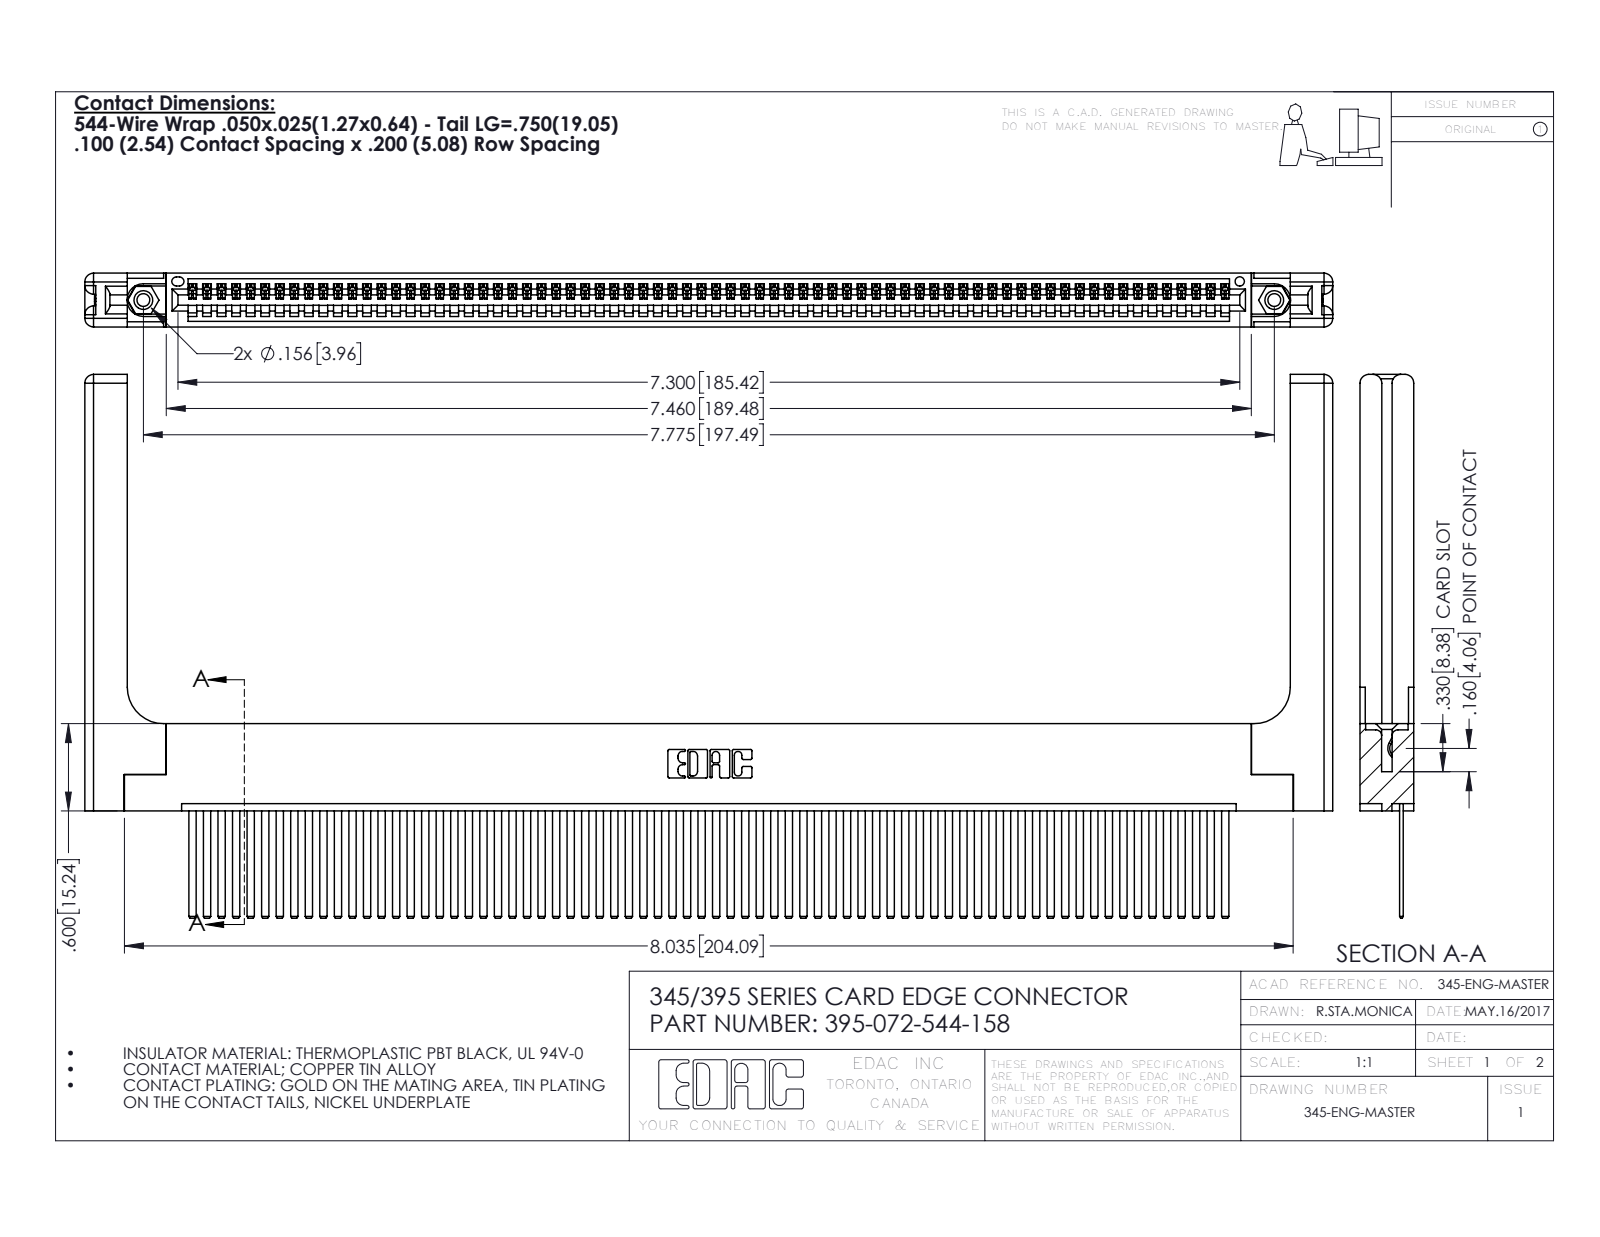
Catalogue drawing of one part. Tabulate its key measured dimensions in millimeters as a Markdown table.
| quantity | value |
| --- | --- |
| part name | 345-250-001_345-250-001-102; 395-072-544-158; 345-220-058_345-220-058; 345 Part_Flush Mounting Lugs - 0.156 Dia-TH (+1 more) |
| STEP written by | SolidWorks 2016 (CONFIG_CONTROL_DESIGN) |
| units | millimeters |
| bodies | 77 solids, 4126 faces (2820 planar, 1246 cylindrical, 60 other) |
| overall size | 217.9 × 94.9 × 9.4 |
| volume | 30 280 mm³ |
| surface area | 37 150 mm² |
| round holes (diameter × count) | 2.3 × 2, 3.2 × 2, 4 × 2, 1.6 × 1 |
| round bosses / shafts (diameter × count) | 3.9 × 2 |
| partial cylindrical surfaces (radius × count) | 0.2 × 144, 0.3 × 22, 1.5 × 16, 0.2 × 6, 0.8 × 6, 0.7 × 3, 0.8 × 2, 0.8 × 2 |
| main face-to-face distances | 1.8, 7.6, 2.5, 6.9, 0.6, 9.4, 5.1, 5.7, 3.8, 3.8 |
| hole center spacings | 6.9, 191.5, 197.5 |
